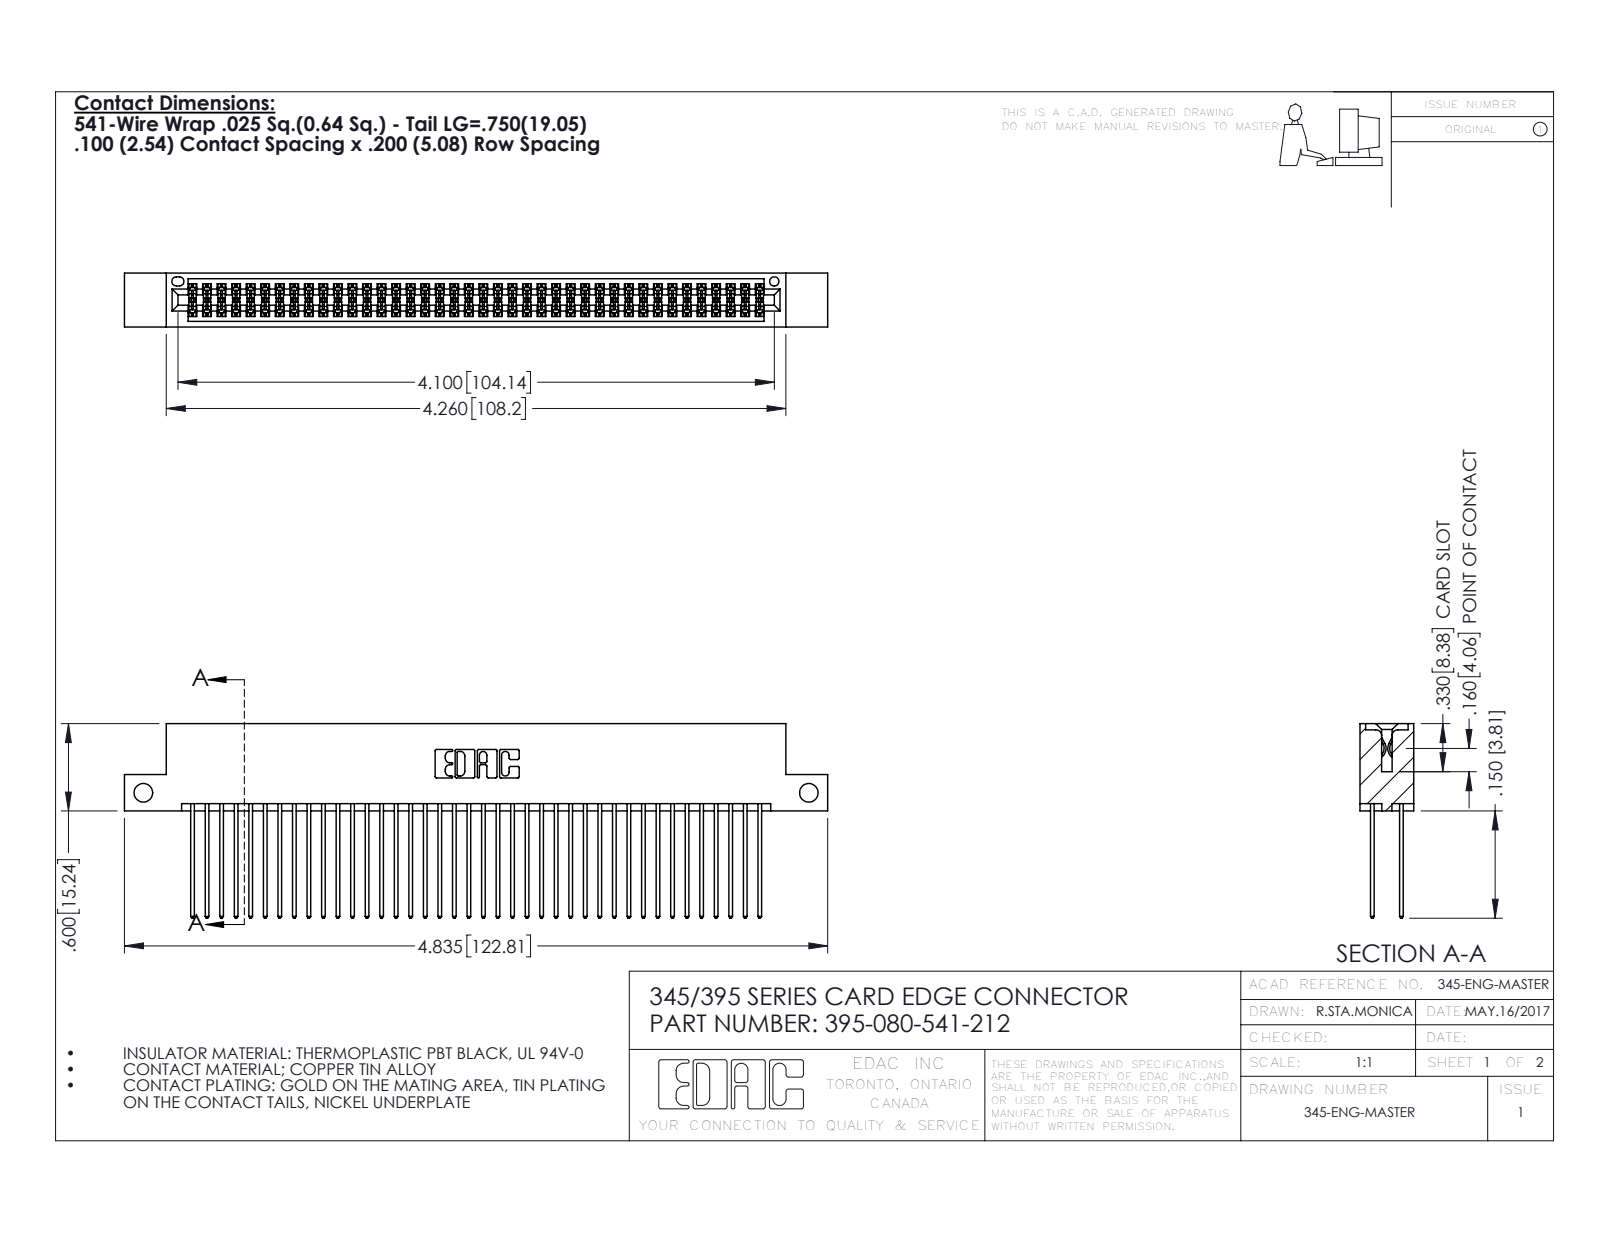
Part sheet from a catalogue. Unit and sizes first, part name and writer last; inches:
Units: inches
Overall size (bounding box): 4.835 × 1.337 × 0.37
Round holes (diameter × count): ⌀0.128 ×2, ⌀0.064 ×1
Partial cylindrical surfaces — rounded edges, fillets, slot ends (radius × count): R0.006 ×120, R0.01 ×80, R0.01 ×22, R0.007 ×6, R0.031 ×6, R0.026 ×3, R0.014 ×2, R0.019 ×2
Main face-to-face distances: 0.298, 0.072, 0.2, 0.098, 0.272, 0.025, 0.225, 0.37, 0.175, 0.149
Hole centre spacings: 4.575
Volume: 0.75 in³ · Surface area: 31.22 in²
Bodies: 81 solids, 4126 faces (2720 planar, 1406 cylindrical, 0 other)
Part name (STEP PRODUCT): 345-292-001_345-293-141; 345 Part_Flush Mounting Lugs - Side Mount; 395-080-541-212
STEP written by: SolidWorks 2016 (CONFIG_CONTROL_DESIGN)
